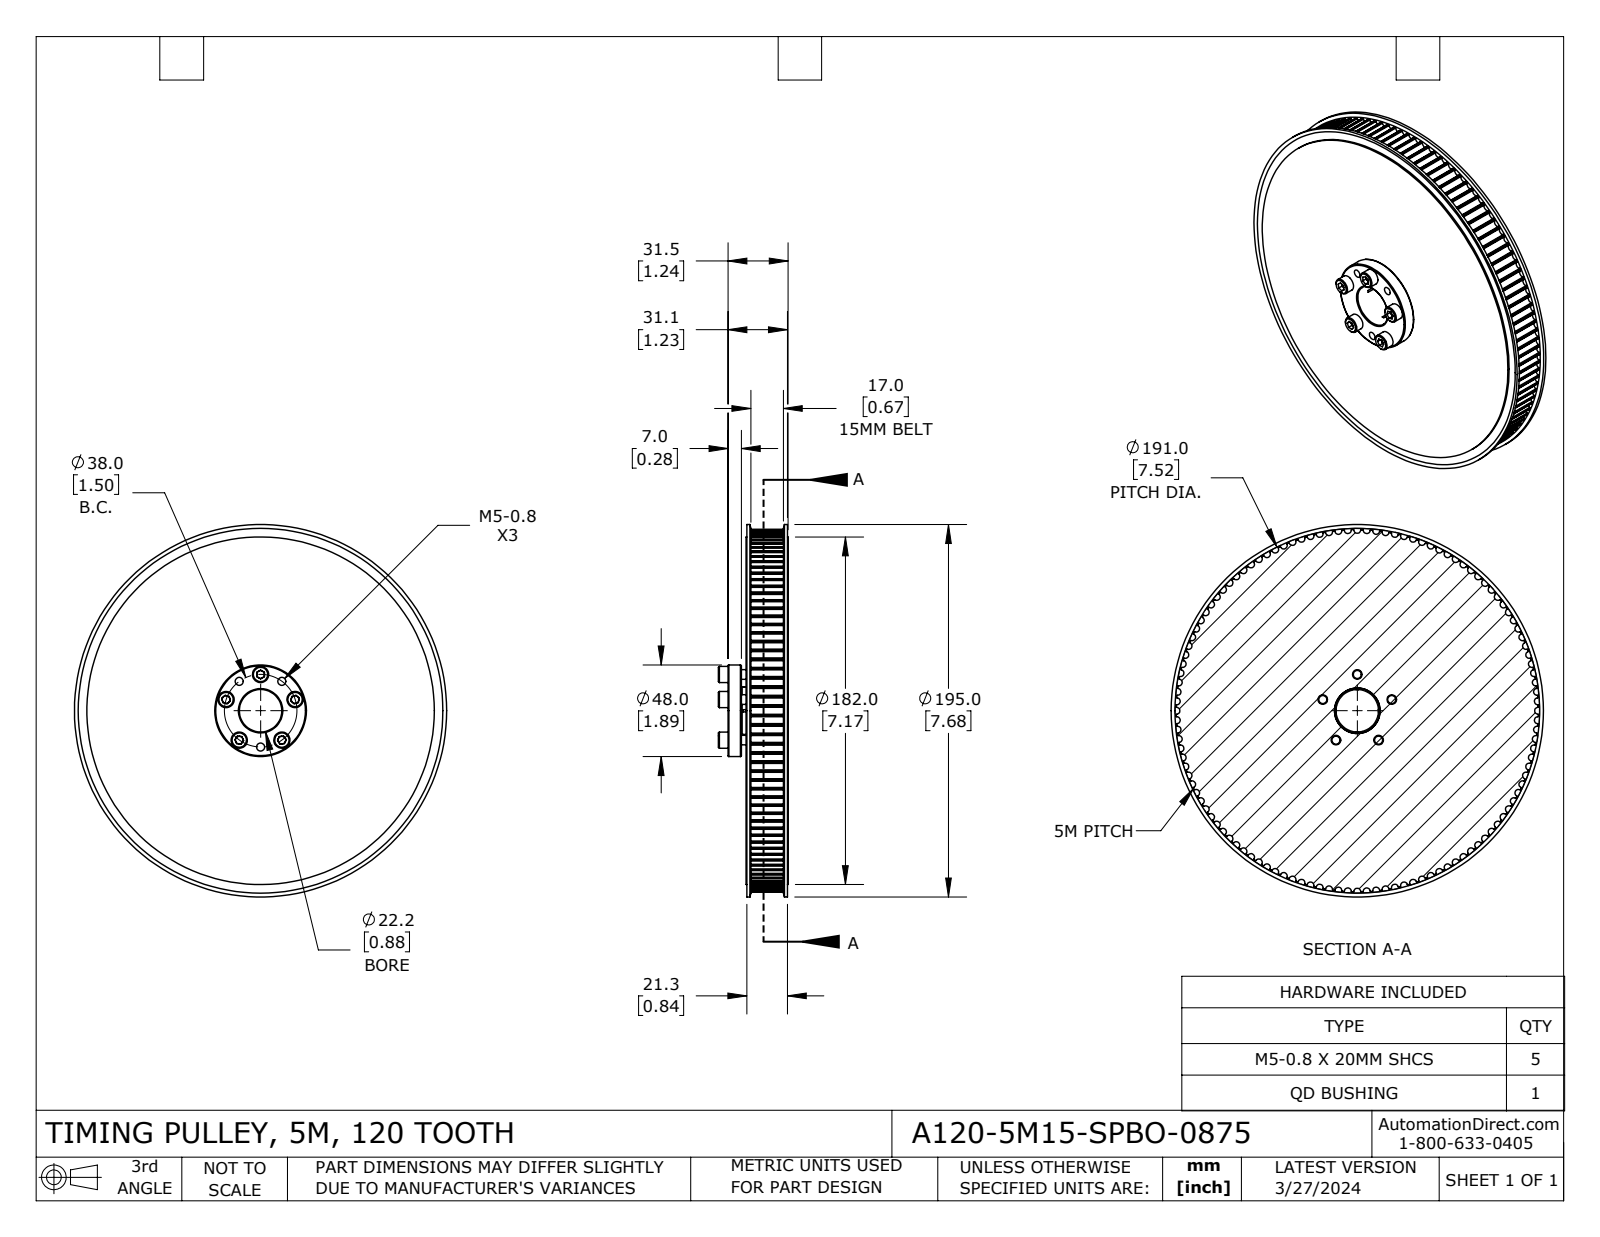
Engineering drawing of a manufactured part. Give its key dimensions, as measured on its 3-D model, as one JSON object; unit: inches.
{"part_name": "A120-5M15-SPBO-0875", "step_written_by": "SolidWorks 2021 (CONFIG_CONTROL_DESIGN)", "units": "inches", "bodies": {"solids": 9, "faces": 830, "planar": 101, "cylindrical": 663, "other": 66}, "overall_size": [7.677, 7.677, 1.437], "volume_in3": 37.46, "surface_area_in2": 161, "round_holes": [[0.165, 8], [0.217, 5], [0.875, 1], [0.978, 1], [7.165, 1]], "round_bosses_or_shafts": [[0.335, 5], [0.197, 5], [7.677, 1], [1.89, 1], [0.977, 1]], "partial_cylinders_radius": [[0.012, 240], [0.072, 120], [3.737, 1]], "face_to_face_distances": [0.866, 0.098, 0.768, 0.035, 0.831, 0.063, 0.732, 0.669, 0.795, 0.472], "hole_center_spacings": [0.748, 1.423, 1.21, 0.463, 0.88, 1.496, 0.462, 0.879]}
